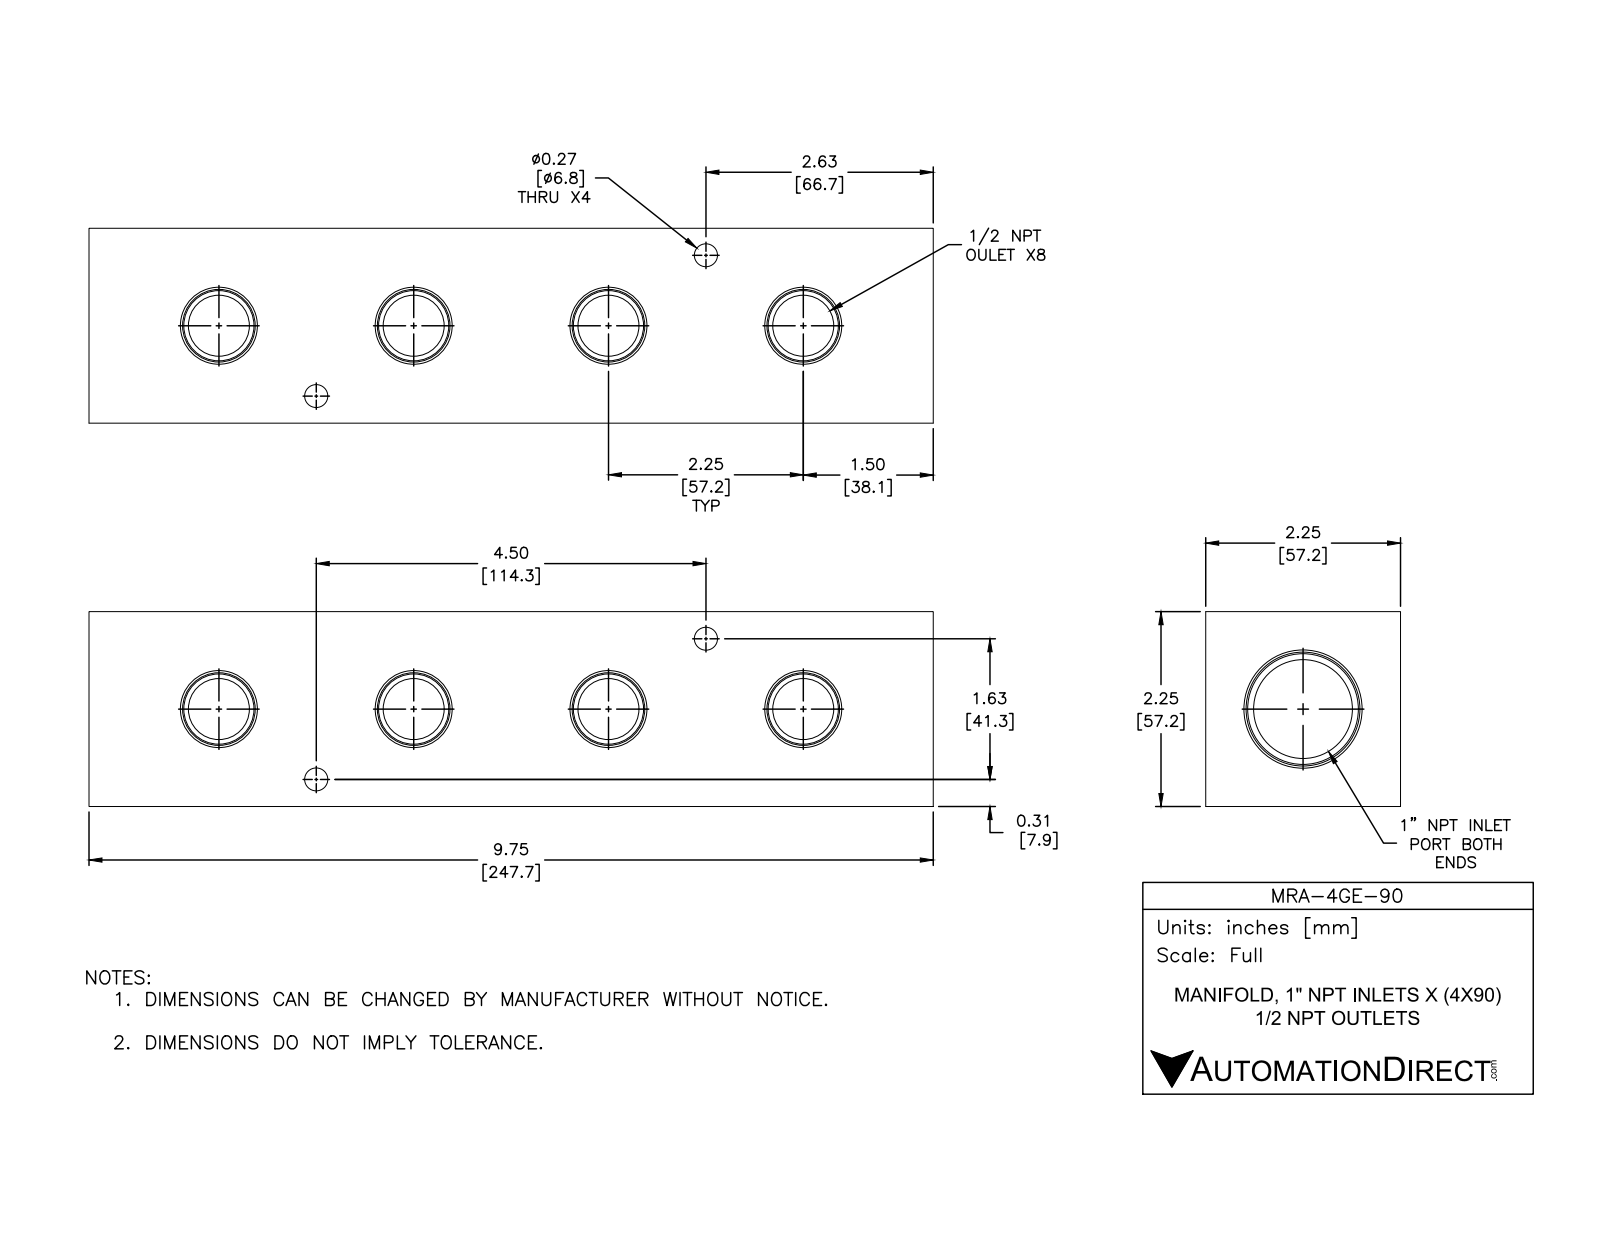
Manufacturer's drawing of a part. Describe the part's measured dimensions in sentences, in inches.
The part is named "MRA-4GE-90". Its 3-D file was written by "SolidWorks 2015 (CONFIG_CONTROL_DESIGN)". It is 1 solid with 90 faces: 16 planar, 34 cylindrical and 40 other. Overall it measures 9.75 by 2.25 by 2.25 inches. Its volume is 36.08 cubic inches and its surface area 143.1 square inches. Round holes: 8 of diameter 0.703, 4 of diameter 0.266, 1 of diameter 1.141. The main face-to-face distances are 2.25, 9.75, 0.53, 1.72, 0.66, 9.09, 8.43. The hole center spacings are 1.388, 2.25, 5.683, 2.25, 3.471, 3.472, 4.5, 4.5.
